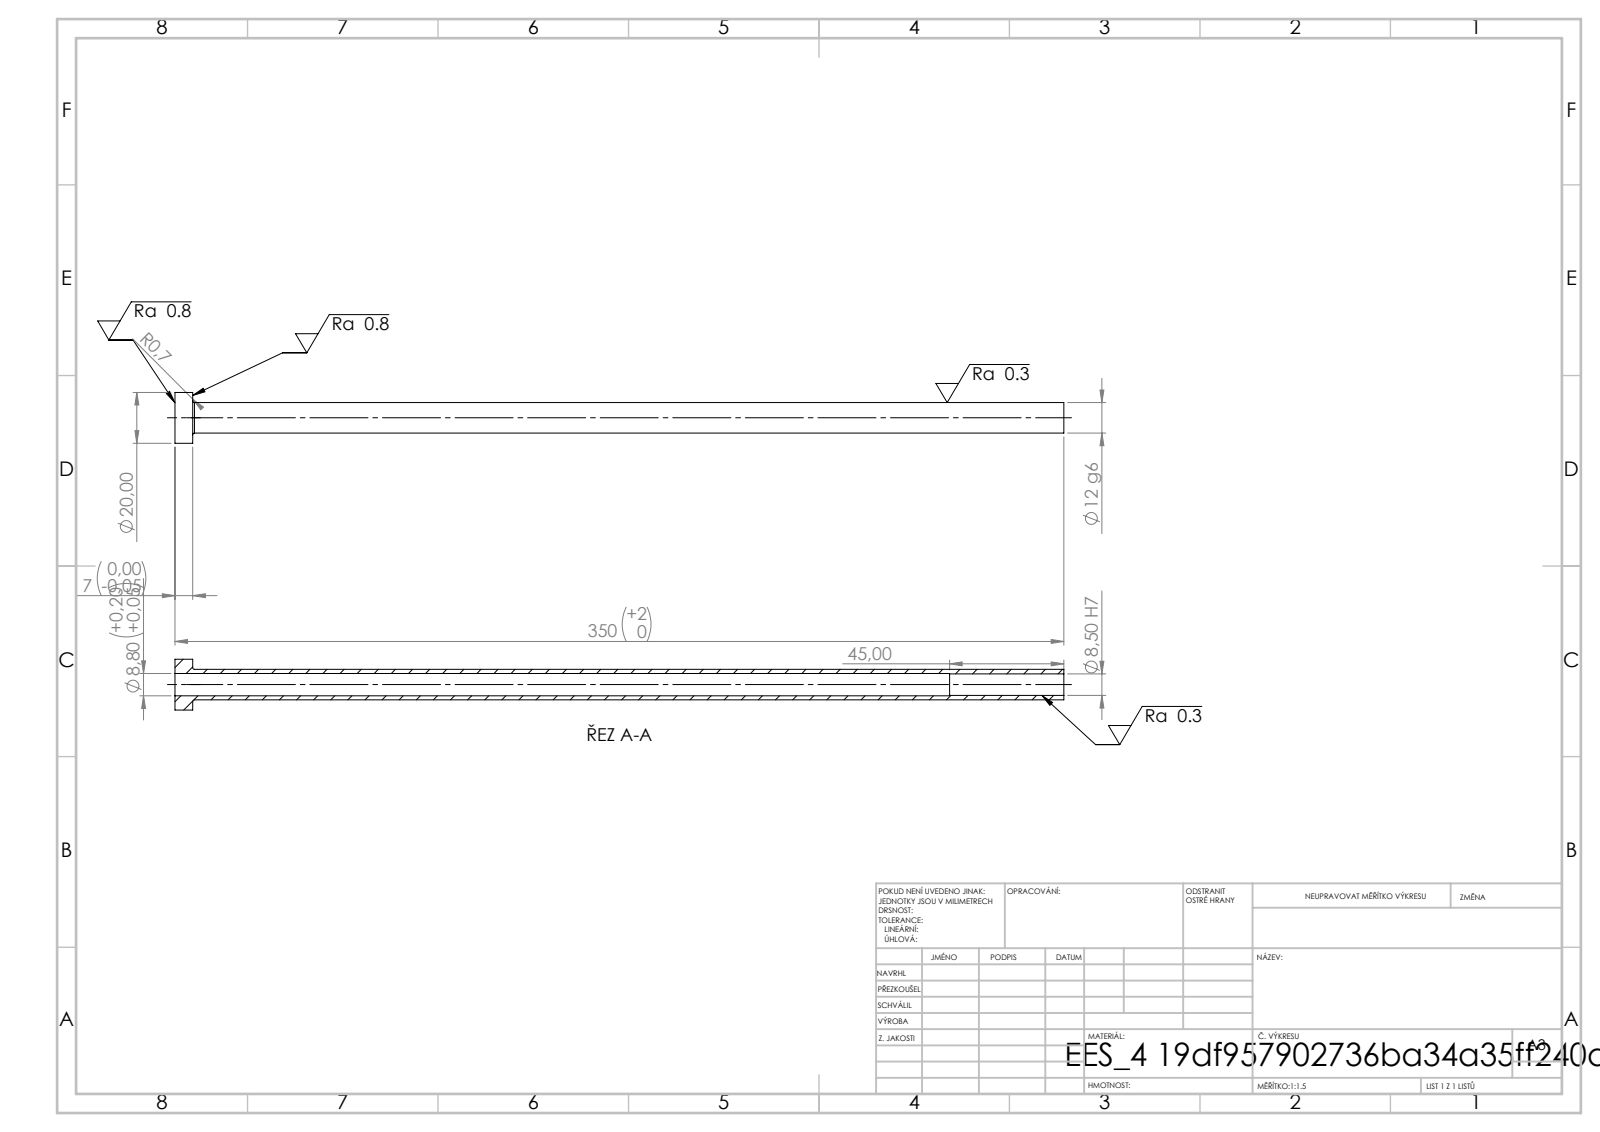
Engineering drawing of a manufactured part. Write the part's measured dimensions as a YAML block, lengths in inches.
step_written_by: "SolidWorks 2019 (CONFIG_CONTROL_DESIGN)"
units: inches
bodies: {solids: 1, faces: 14, planar: 4, cylindrical: 8, other: 2}
overall_size: [13.78, 0.787, 0.787]
volume: 1.214
surface_area: 36.44
round_holes:
  - {diameter: 0.335, count: 1}
  - {diameter: 0.346, count: 1}
round_bosses_or_shafts:
  - {diameter: 0.787, count: 1}
  - {diameter: 0.472, count: 1}
face_to_face_distances: [0.276, 13.78, 13.504, 12.008, 11.732, 1.772]
